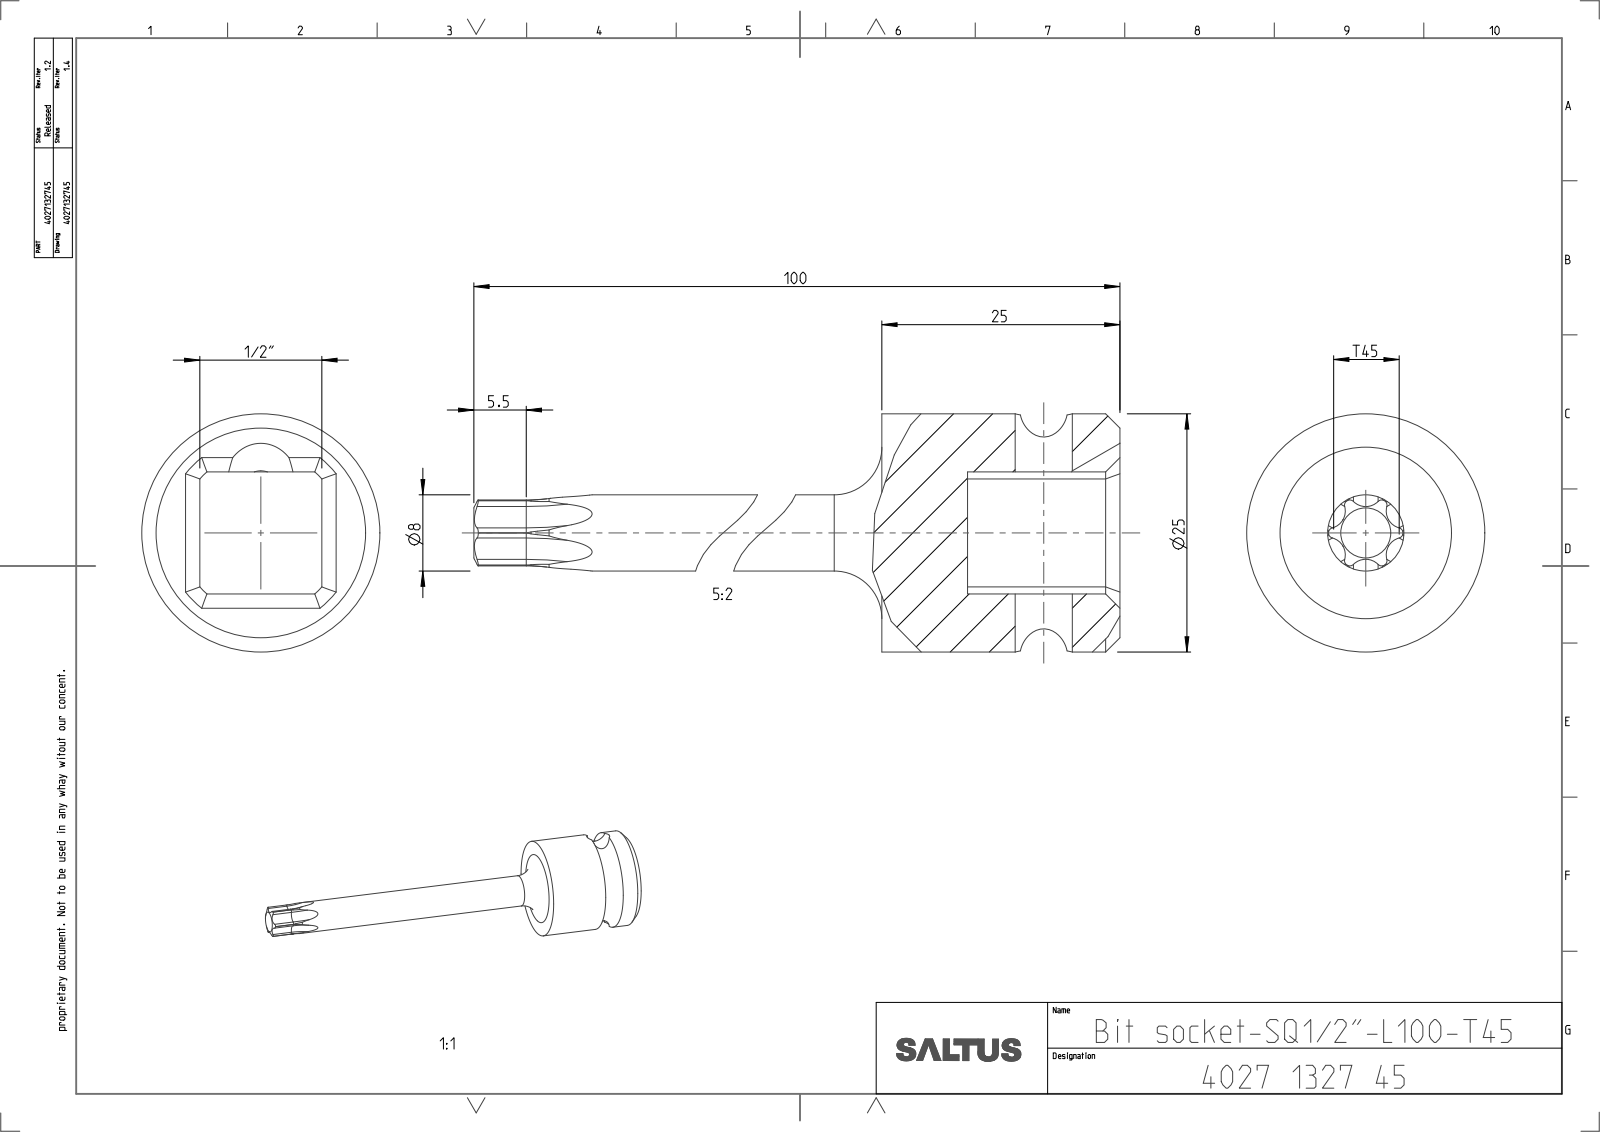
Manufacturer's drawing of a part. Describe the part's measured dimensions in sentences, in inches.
The part is named "4027132745". Its 3-D file was written by "CREO PARAMETRIC BY PTC INC, 2022414 (CONFIG_CONTROL_DESIGN)". It is 1 solid with 88 faces: 13 planar, 39 cylindrical and 36 other. Overall it measures 3.937 by 0.984 by 0.984 inches. Its volume is 0.761 cubic inches and its surface area 8.699 square inches. Round holes: 1 of diameter 0.236. Round bosses or shafts: 1 of diameter 0.984, 1 of diameter 0.315. Partial cylindrical surfaces (rounded edges, fillets, slot ends): 12 of radius 0.021, 6 of radius 0.072, 1 of radius 0.154, 1 of radius 0.157, 1 of radius 0.337. The main face-to-face distances are 0.505, 0.354, 0.63, 0.984, 3.937, 3.307, 2.953.
